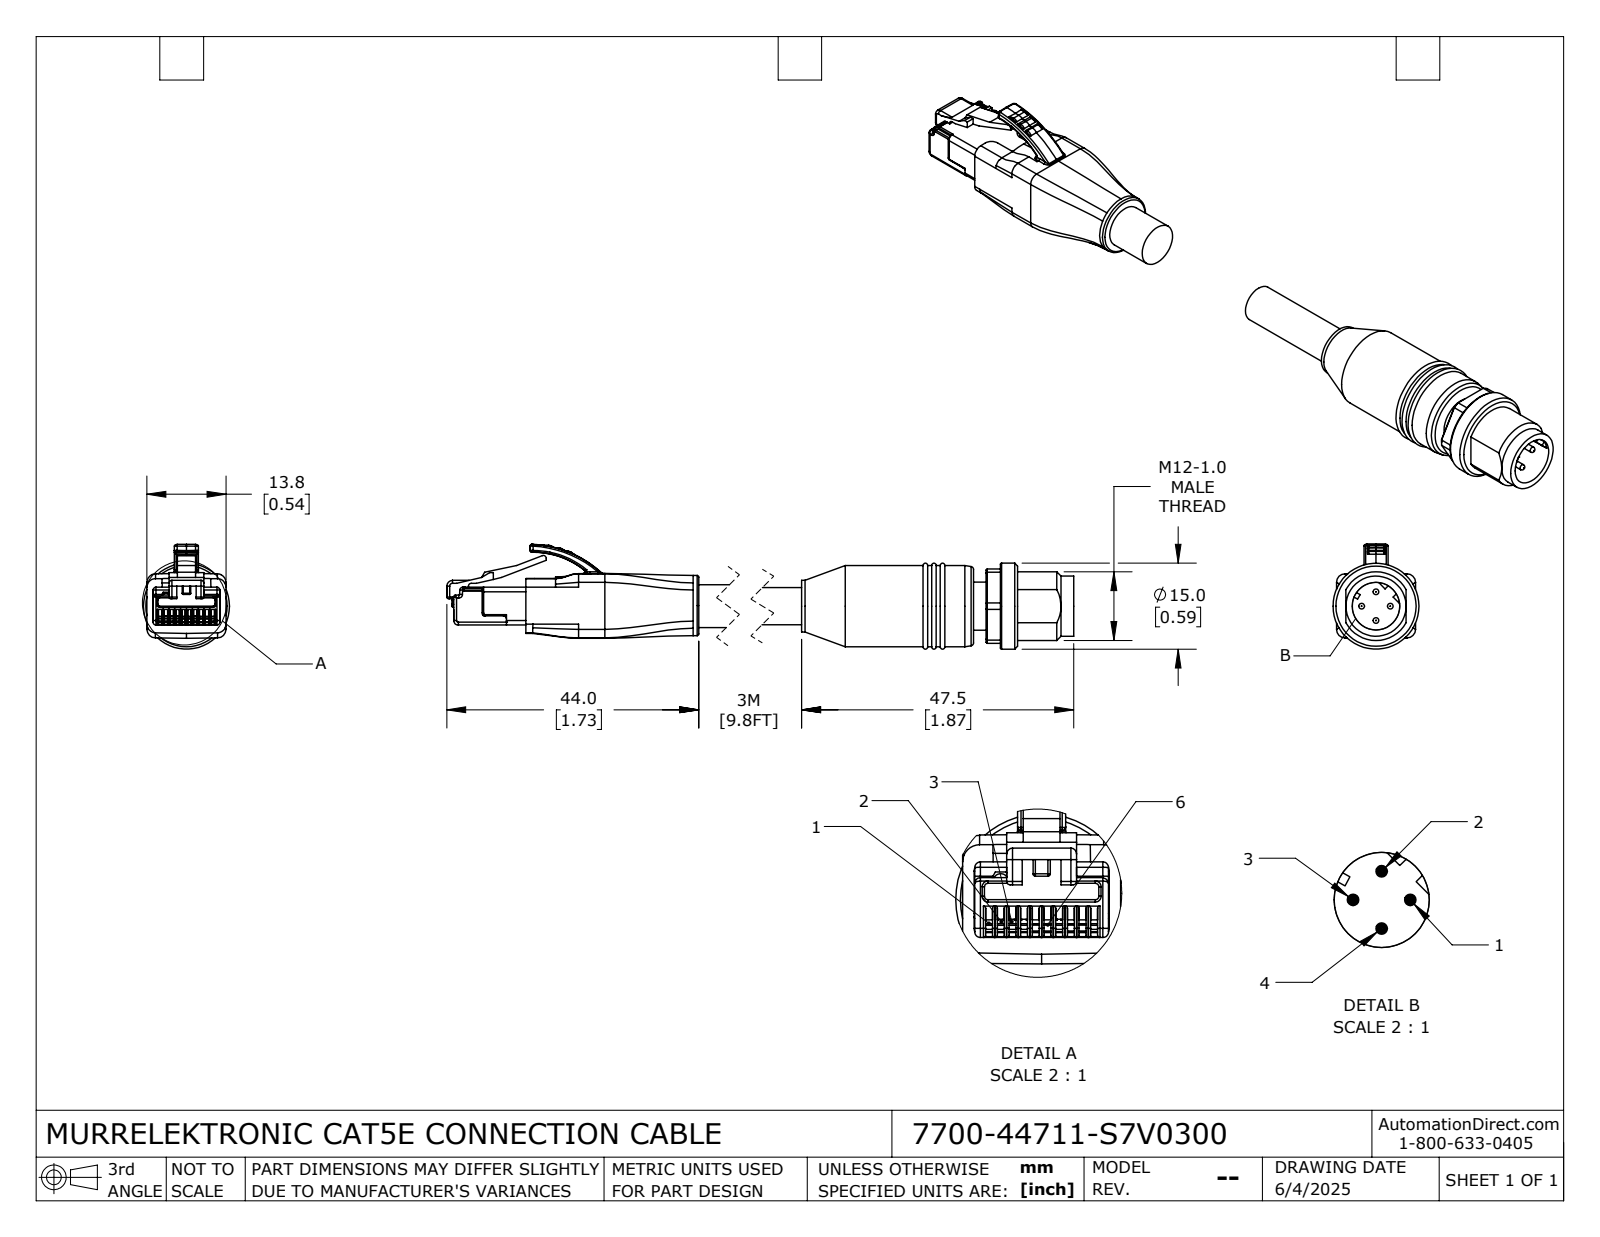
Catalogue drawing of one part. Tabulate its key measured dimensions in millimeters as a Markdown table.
| quantity | value |
| --- | --- |
| part name | 7700-44711-S7V0300; 7700-44711-S7V0300_MALE; 7700-44711-S7V0300_RJ45 |
| STEP written by | SolidWorks 2024 (CONFIG_CONTROL_DESIGN) |
| units | millimeters |
| bodies | 2 solids, 757 faces (357 planar, 235 cylindrical, 165 other) |
| overall size | 144.5 × 18.29 × 15 |
| volume | 11 873 mm³ |
| surface area | 5 775 mm² |
| round holes (diameter × count) | 8.3 × 1 |
| round bosses / shafts (diameter × count) | 1 × 4, 10.5 × 2, 15 × 1, 14.2 × 1, 9 × 1, 8.4 × 1, 7.5 × 1, 6.5 × 1 |
| partial cylindrical surfaces (radius × count) | 0.2 × 61, 0.5 × 25, 0.3 × 14, 1.5 × 9, 0.8 × 5, 0.54 × 2, 5 × 2, 0.13 × 1 |
| main face-to-face distances | 13.8, 2.2, 1.65, 12.15, 1.01, 12.79, 0.64, 11.14, 9.8, 0.9 |
